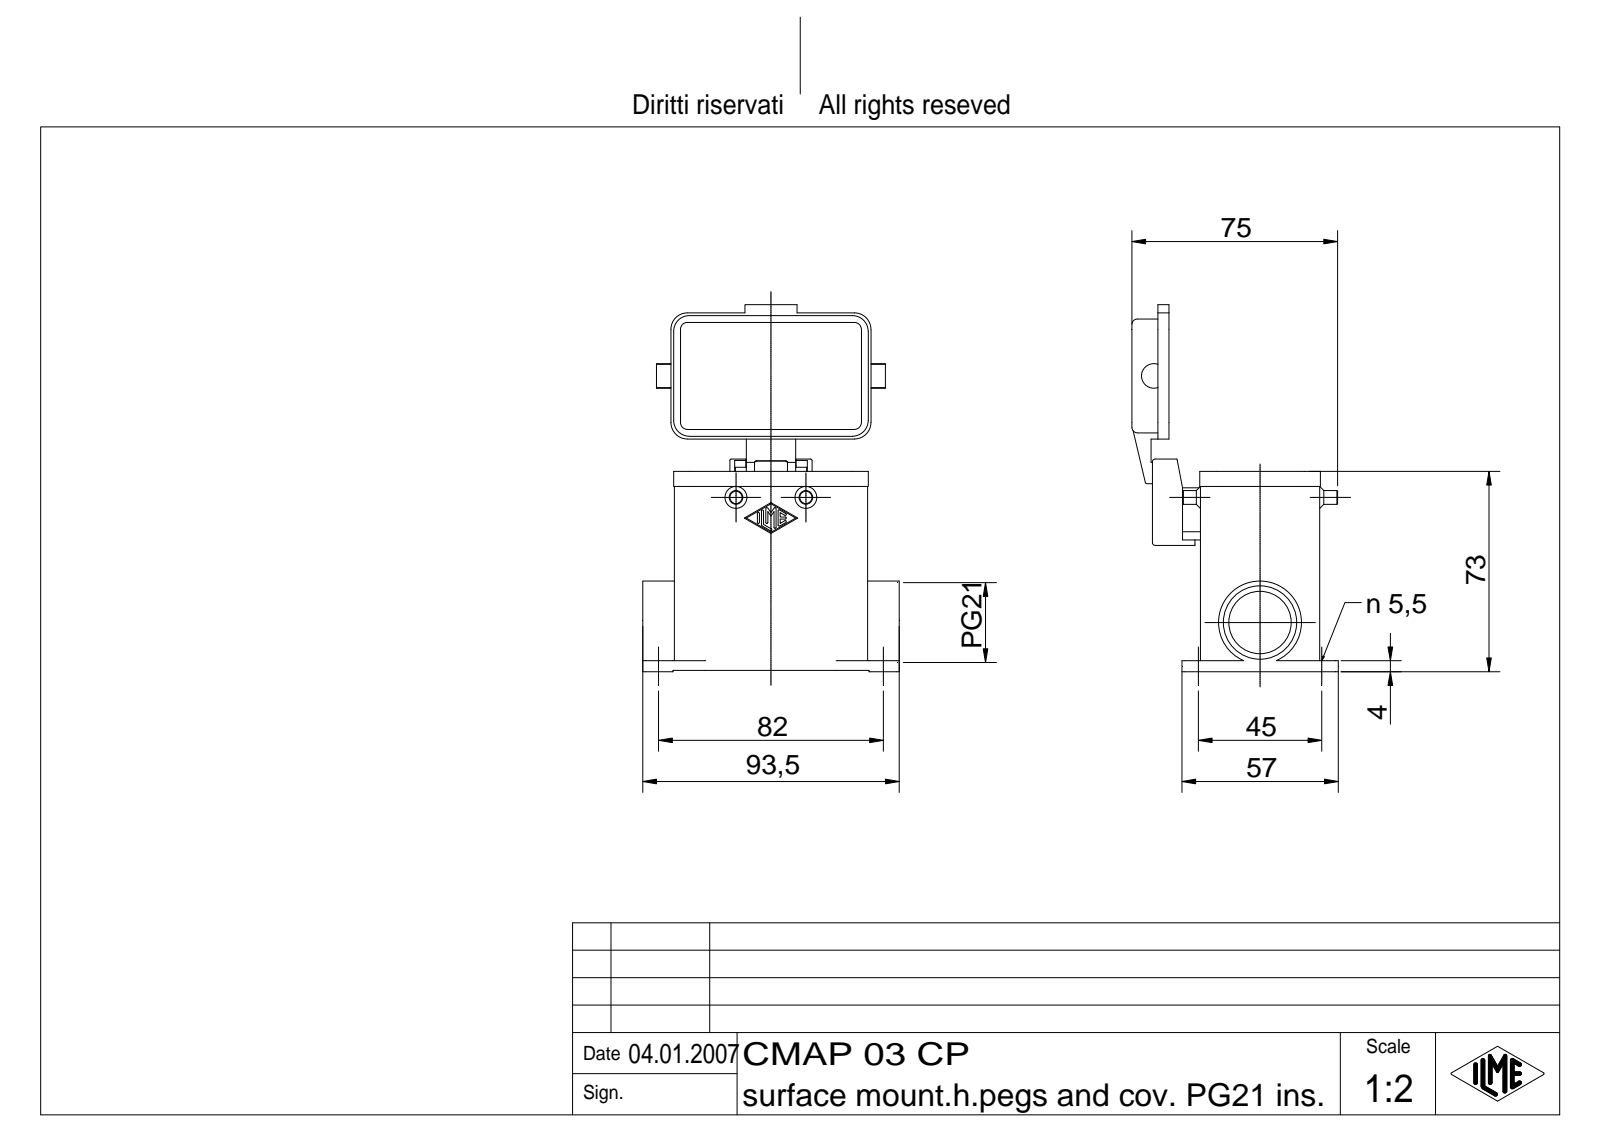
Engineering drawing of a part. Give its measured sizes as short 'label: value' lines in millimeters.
name: CMAP 03 CP
written by: Autodesk Inventor 7 (AUTOMOTIVE_DESIGN)
unit: mm
bodies: 1 solid, 470 faces (193 planar, 166 cylindrical, 111 other)
size: 133.75 × 93.5 × 75.25
volume: 105 618 mm³; area: 61 206 mm²
holes: 4× ⌀5.5, 1× ⌀4, 1× ⌀5, 1× ⌀22.78, 1× ⌀26.78
bosses: 2× ⌀5, 2× ⌀3, 1× ⌀30.28, 1× ⌀7, 1× ⌀4
rounds: 14× R0.38, 14× R1, 12× R6, 10× R0.5, 8× R0.7, 8× R2, 4× R2.5, 4× R3
face distances: 3, 40.5, 43.5, 2.5, 68.5, 37.5, 22.5, 66, 3.5, 63
hole spacings: 45, 82, 93.54
